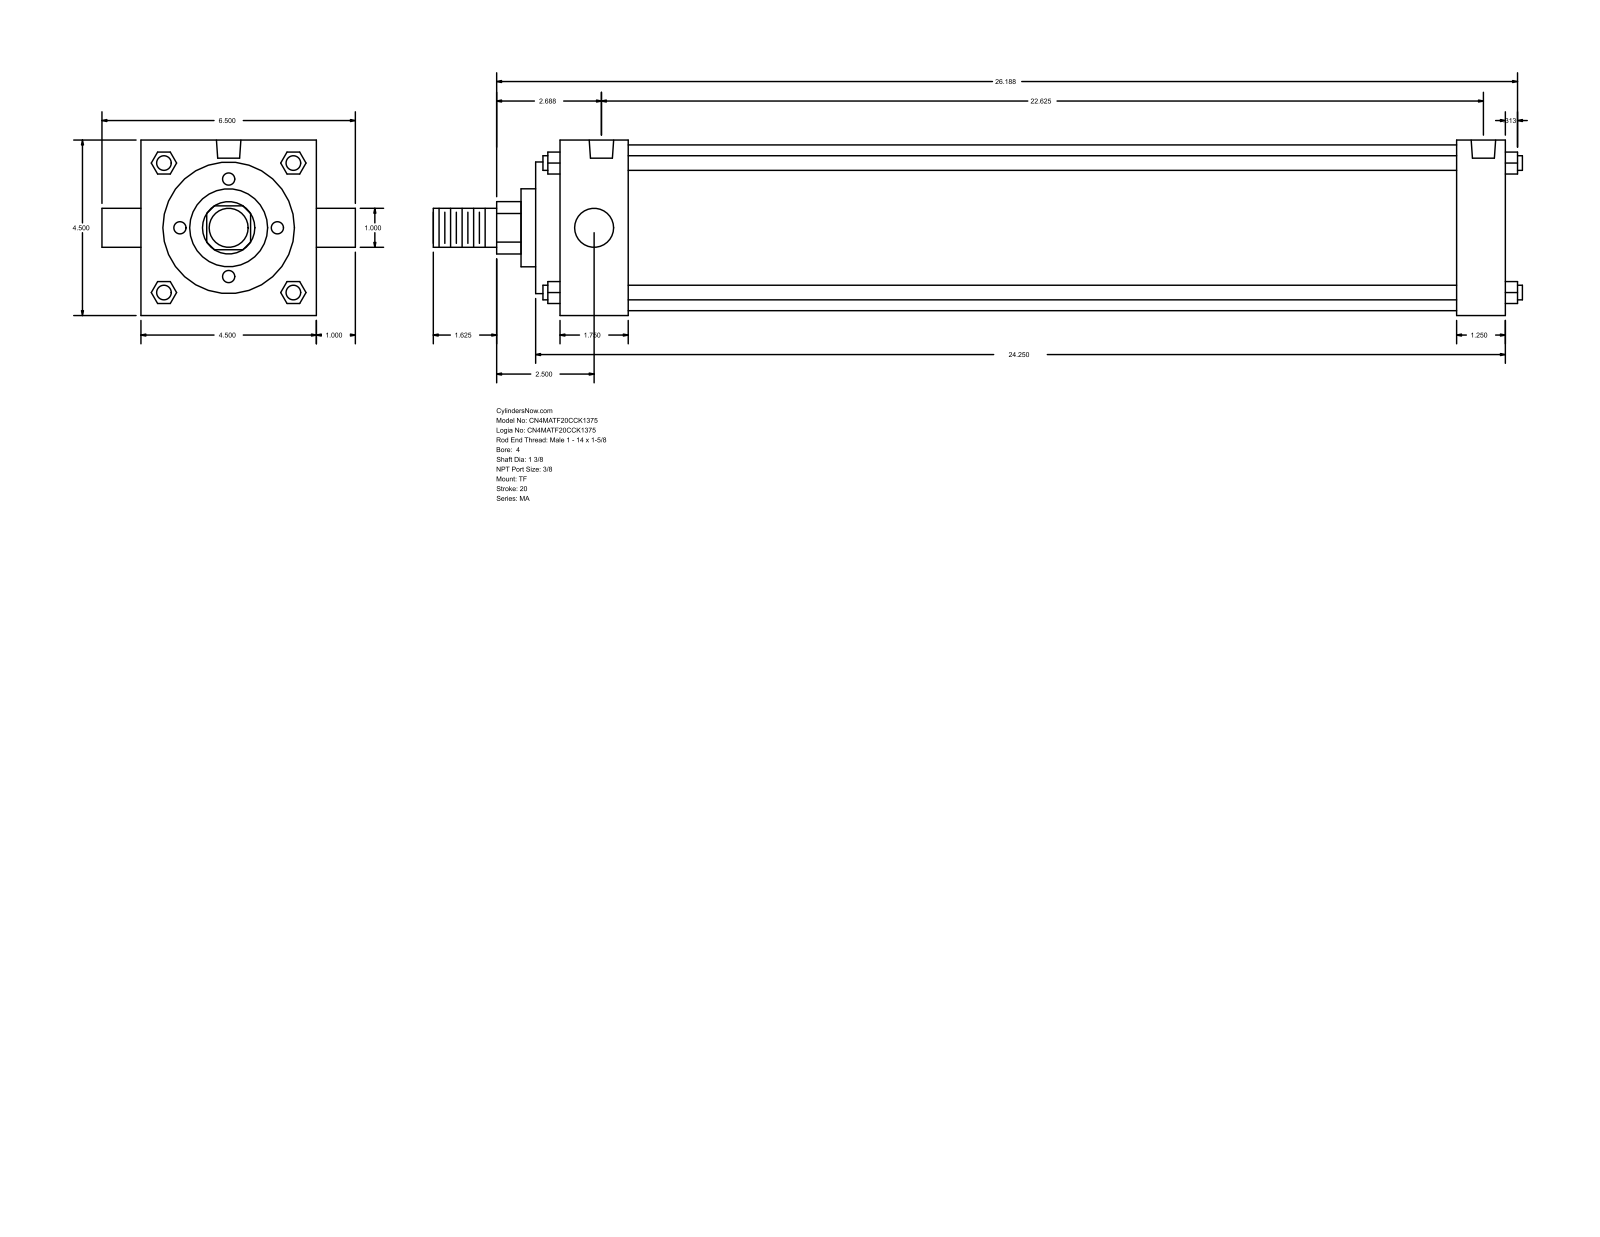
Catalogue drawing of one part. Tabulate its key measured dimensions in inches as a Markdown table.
| quantity | value |
| --- | --- |
| part name | MA_TF__0400_1.375 |
| STEP written by | GSSL Pune (CONFIG_CONTROL_DESIGN) |
| units | inches |
| bodies | 0 solids, 122 faces (93 planar, 29 cylindrical, 0 other) |
| overall size | 27.937 × 6.5 × 4.5 |
| round holes (diameter × count) | 0.437 × 3, 0.627 × 2 |
| round bosses / shafts (diameter × count) | 0.375 × 4, 1 × 2, 4.25 × 1, 3.375 × 1, 2 × 1, 1.375 × 1 |
| partial cylindrical surfaces (radius × count) | 0.672 × 1 |
| main face-to-face distances | 4.5, 24.25, 0.625, 24.875, 23.625, 23, 1.25, 2.375, 1.75, 21.25 |
| hole center spacings | 0.188, 22.437, 22.25, 22.625 |
